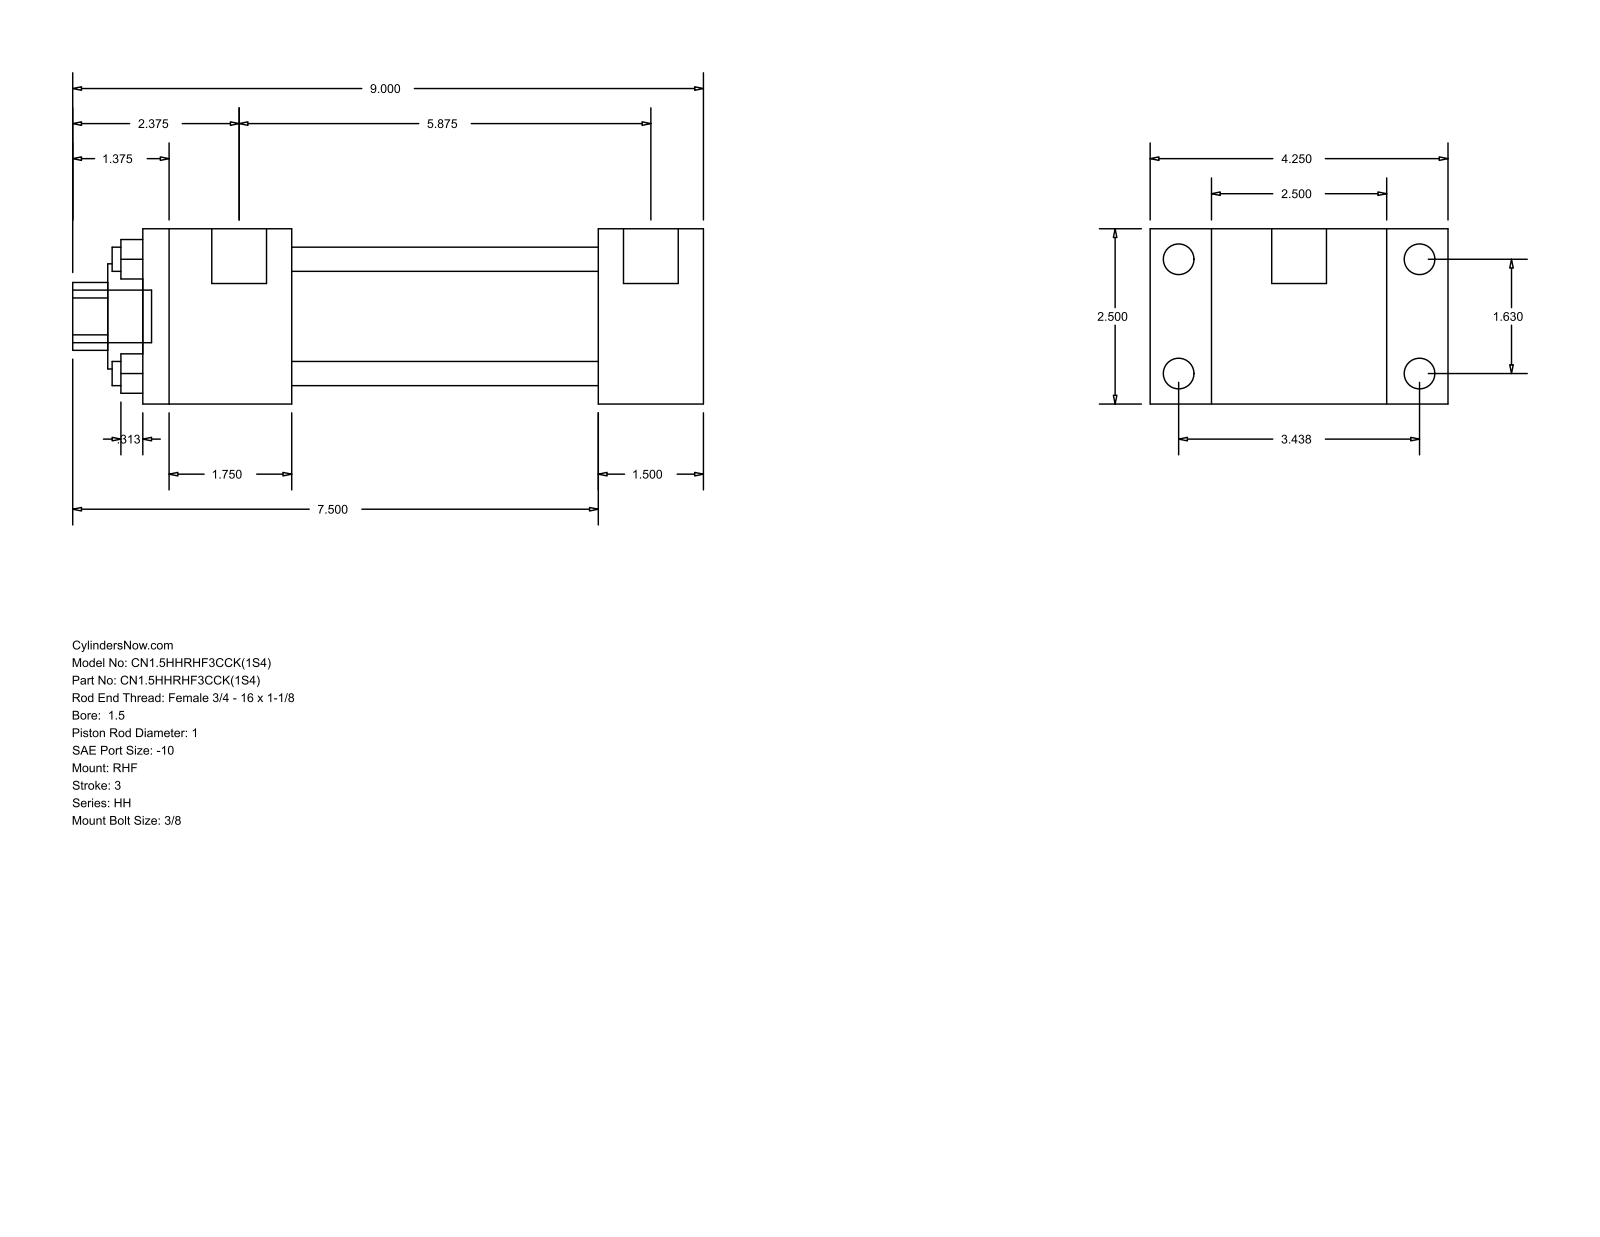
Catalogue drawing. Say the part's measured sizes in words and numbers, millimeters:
The part is named "HH_RHF__0150_1". Its 3-D file was written by "GSSL Pune (CONFIG_CONTROL_DESIGN)". It is 0 solids with 88 faces: 60 planar, 28 cylindrical and 0 other. Overall it measures 228.6 by 107.95 by 63.5 millimeters. Round holes: 4 of diameter 8.76, 1 of diameter 25.4, 1 of diameter 38.1, 1 of diameter 44.45. Round bosses or shafts: 4 of diameter 11.13, 4 of diameter 5.56, 2 of diameter 19.84, 1 of diameter 19.05. Partial cylindrical surfaces (rounded edges, fillets, slot ends): 1 of radius 12.29. The main face-to-face distances are 63.5, 22.23, 85.73, 38.1, 107.96, 111.12, 149.22, 53.98, 165.1, 203.2. The hole center spacings are 29.27, 41.4, 58.55.
